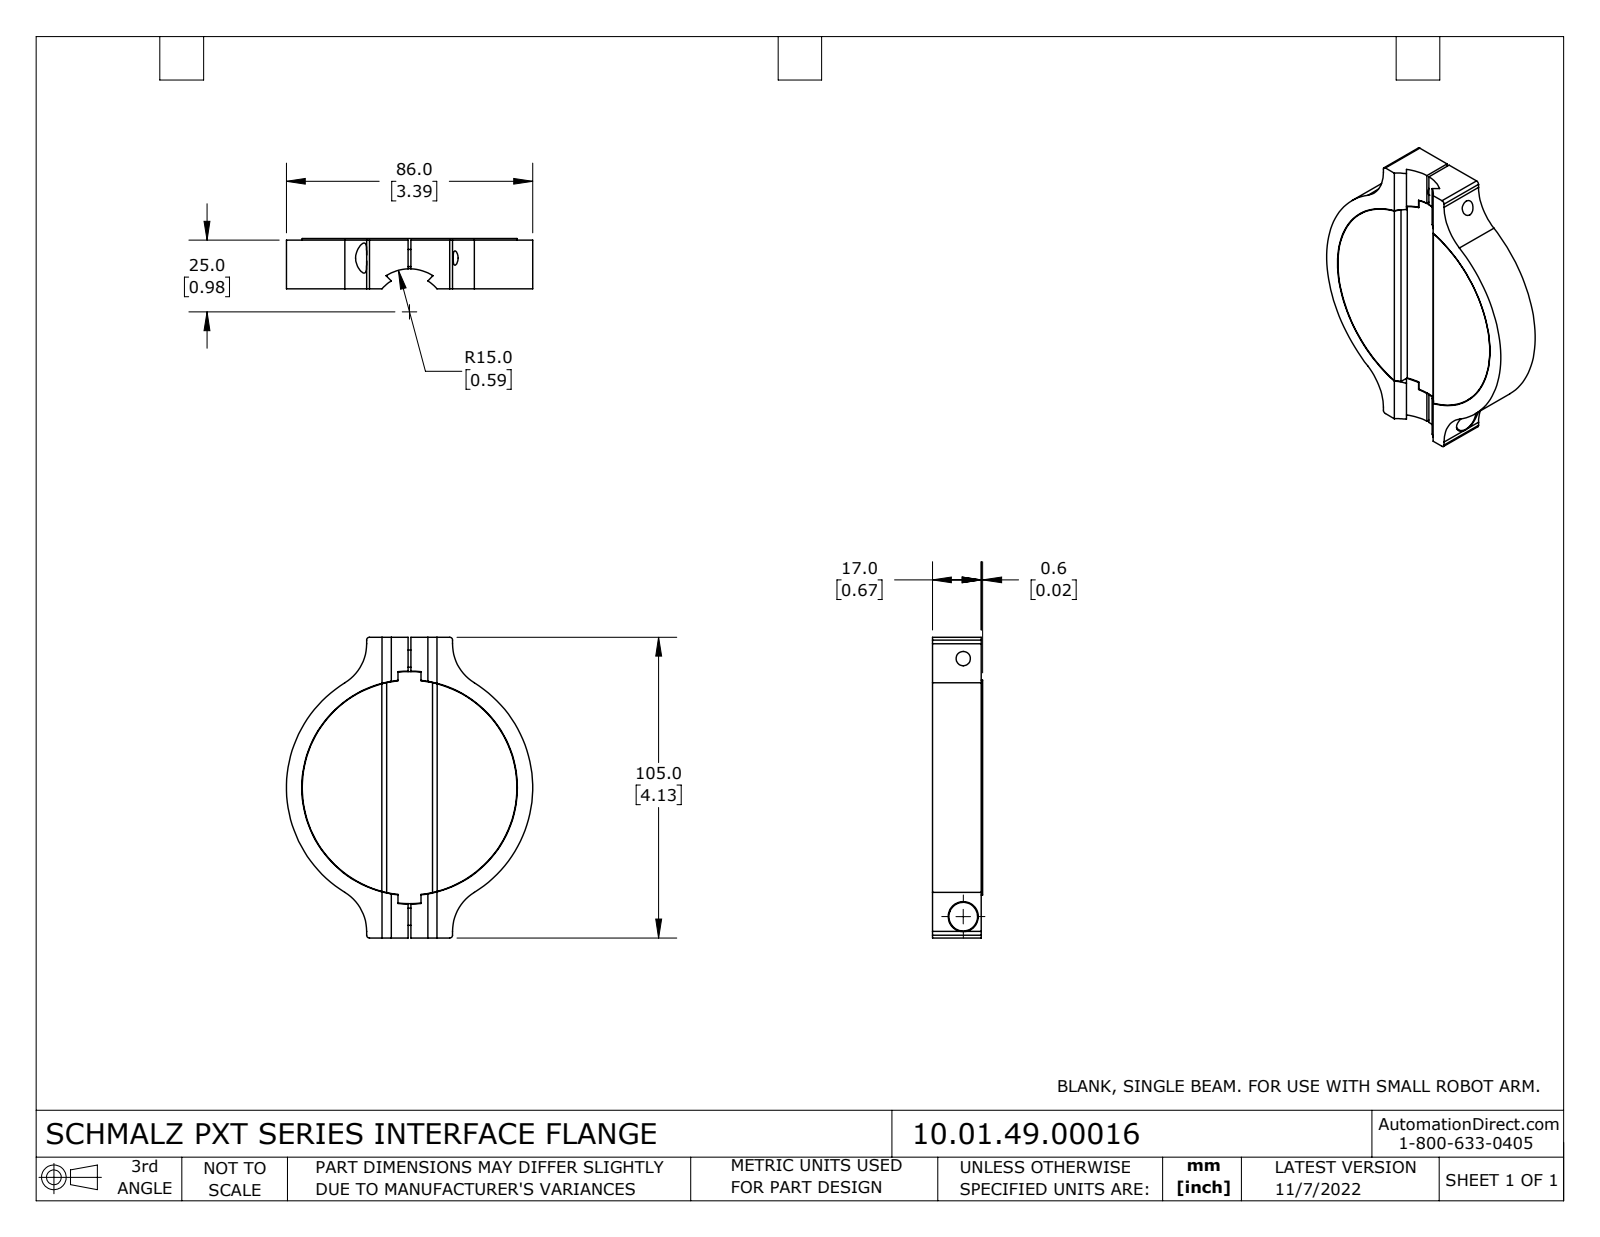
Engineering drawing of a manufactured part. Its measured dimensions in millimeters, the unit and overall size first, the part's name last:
Units: millimetres
Overall size (bounding box): 105 × 86 × 17.55
Round holes (diameter × count): ⌀5 ×2, ⌀6.3 ×2, ⌀10.5 ×2, ⌀75.3 ×1, ⌀81.3 ×1
Round bosses / shafts (diameter × count): ⌀10 ×2, ⌀6 ×2, ⌀81 ×1, ⌀75 ×1
Partial cylindrical surfaces — rounded edges, fillets, slot ends (radius × count): R1 ×4, R16 ×4, R12.5 ×1, R12.55 ×1, R15 ×1, R15.05 ×1, R43 ×1
Main face-to-face distances: 17.5, 16.95, 0.55, 9.5, 17, 7.45, 8, 9.55, 17.55, 3
Hole centre spacings: 90.1
Volume: 100 596 mm³ · Surface area: 32 632 mm²
Bodies: 5 solids, 98 faces (40 planar, 58 cylindrical, 0 other)
Part name (STEP PRODUCT): 10.01.49.00016
STEP written by: SolidWorks 2021 (CONFIG_CONTROL_DESIGN)
